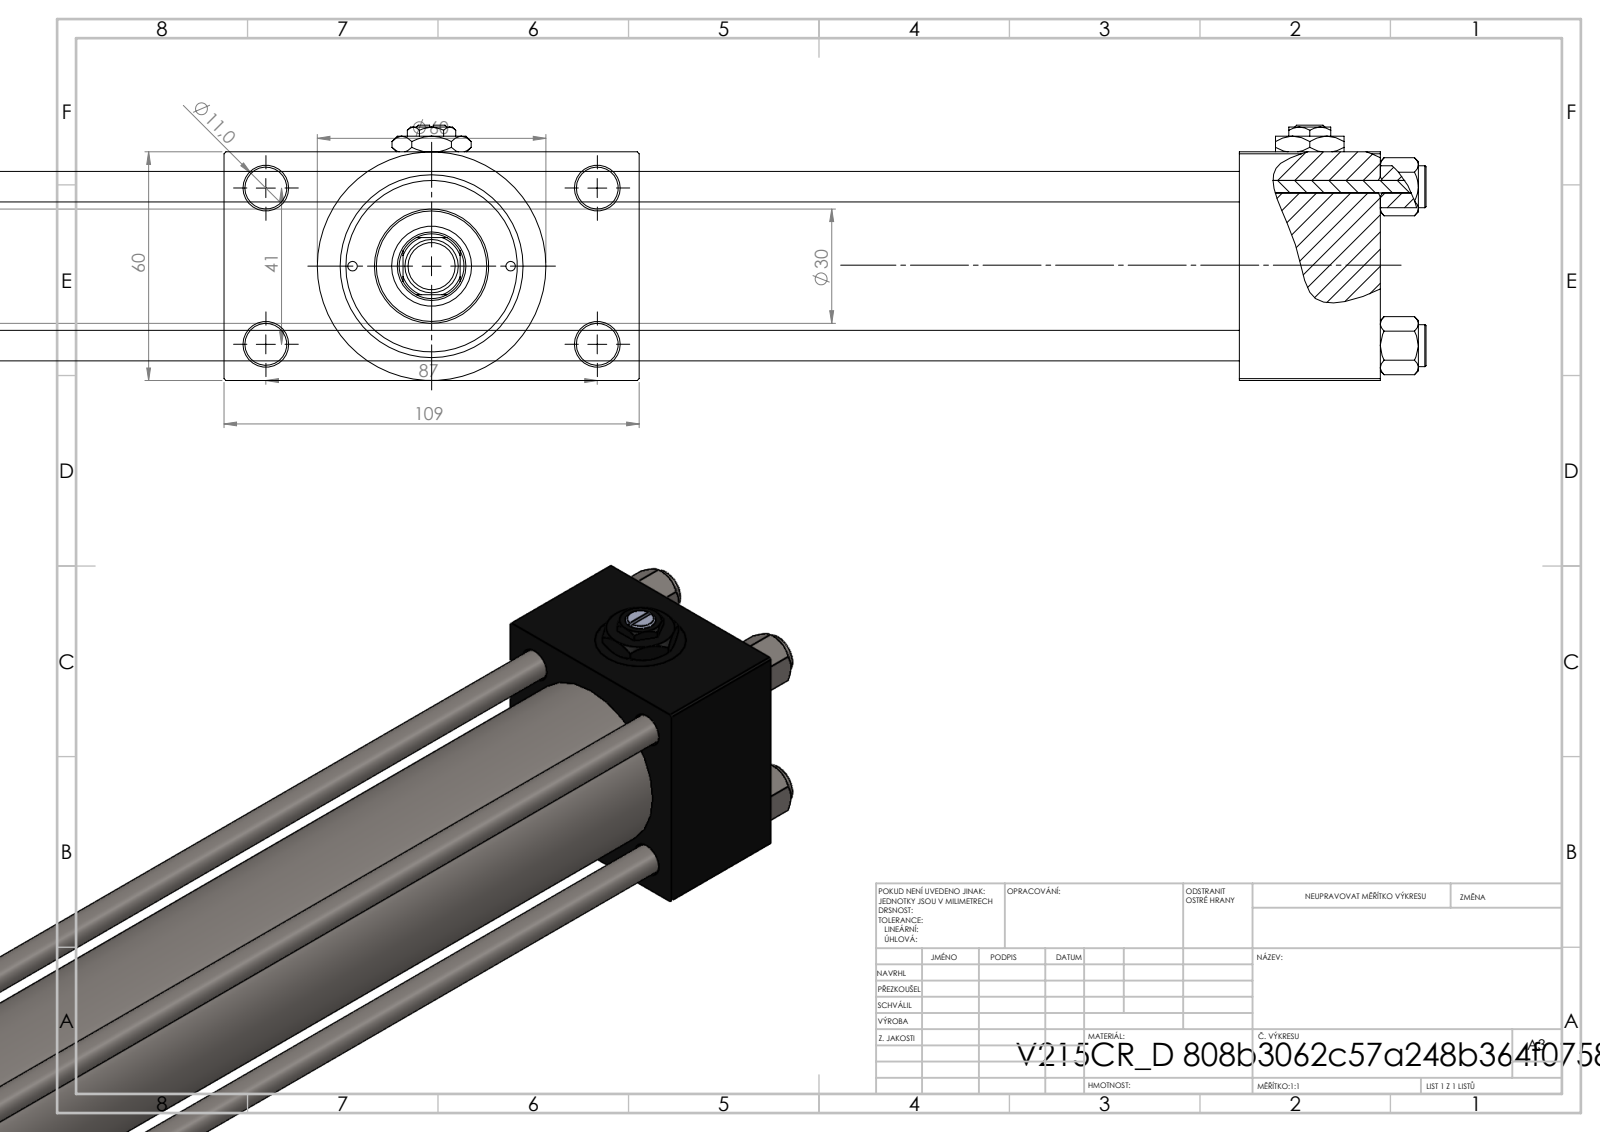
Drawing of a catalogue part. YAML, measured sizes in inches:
part_name: "V215CR_VCP_D; V215CR_D_Body; Zatka_pro_OIL_PORT; V215CR_D_TYCINKA (+3 more)"
step_written_by: "SolidWorks 2019 (CONFIG_CONTROL_DESIGN)"
units: inches
bodies: {solids: 14, faces: 1227, planar: 552, cylindrical: 107, other: 568}
overall_size: [19.016, 4.291, 2.638]
volume: 46
surface_area: 381.2
round_holes:
  - {diameter: 0.315, count: 4}
  - {diameter: 0.433, count: 4}
  - {diameter: 0.656, count: 4}
  - {diameter: 0.945, count: 4}
  - {diameter: 0.276, count: 3}
  - {diameter: 0.098, count: 2}
  - {diameter: 0.335, count: 1}
  - {diameter: 0.709, count: 1}
  - {diameter: 0.827, count: 1}
  - {diameter: 1.22, count: 1}
  - {diameter: 1.575, count: 1}
  - {diameter: 1.772, count: 1}
round_bosses_or_shafts:
  - {diameter: 0.433, count: 4}
  - {diameter: 2.362, count: 1}
  - {diameter: 1.811, count: 1}
  - {diameter: 1.181, count: 1}
  - {diameter: 0.551, count: 1}
  - {diameter: 0.472, count: 1}
partial_cylinders:
  - {radius: 0.335, count: 1}
face_to_face_distances: [2.362, 13.307, 0.965, 3.327, 1.457, 14.764, 1.693, 16.457, 15, 2.087]
hole_center_spacings: [0.821, 0.892, 1.161, 1.206, 1.642, 1.832, 1.856, 1.893]
